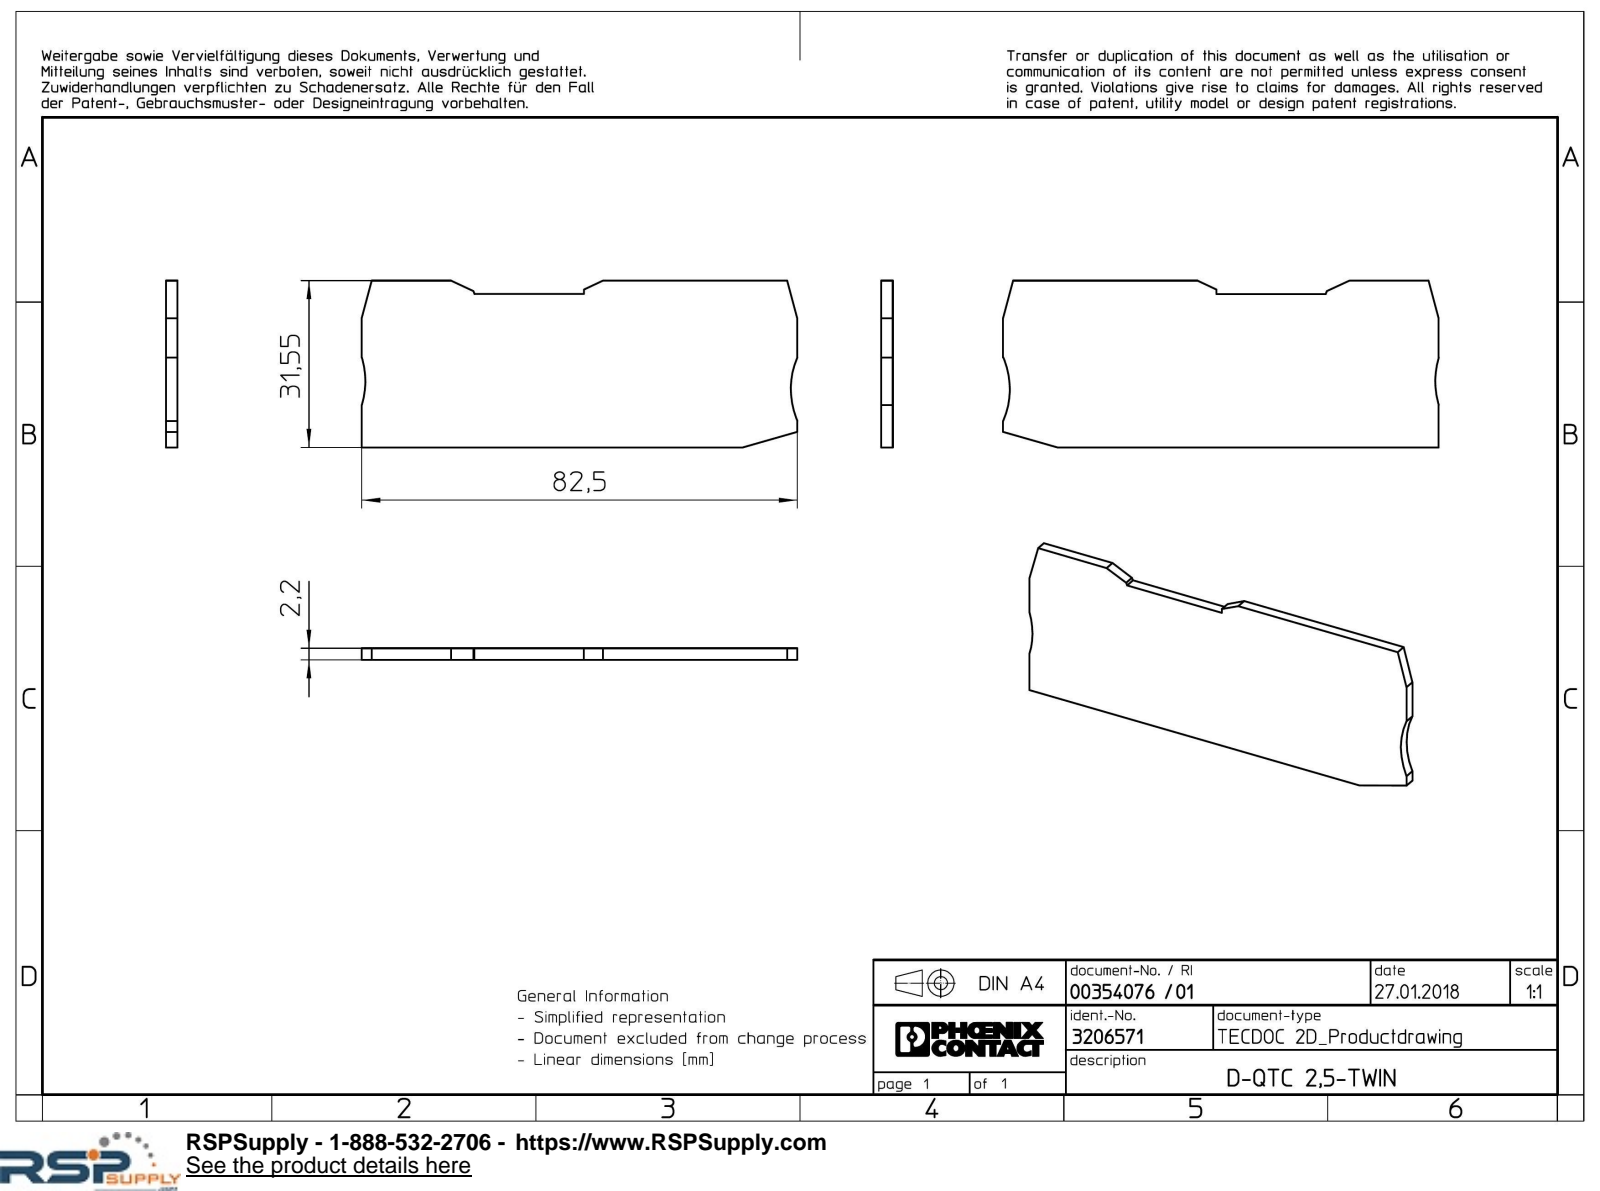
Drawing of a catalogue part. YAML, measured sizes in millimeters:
part_name: "D-QTC_2.5-TWIN-select"
step_written_by: "Creo Elements/Direct Modeling 18.1I 14-Aug-2016 (C) Parametric Technology GmbH (AUTOMOTIVE_DESIGN)"
units: millimeters
bodies: {solids: 1, faces: 19, planar: 17, cylindrical: 2, other: 0}
overall_size: [82.5, 31.55, 2.2]
volume: 5501
surface_area: 5495
partial_cylinders:
  - {radius: 15, count: 2}
face_to_face_distances: [2.2, 31.55, 29.05, 2.5, 82.5, 42.1, 40.4]
